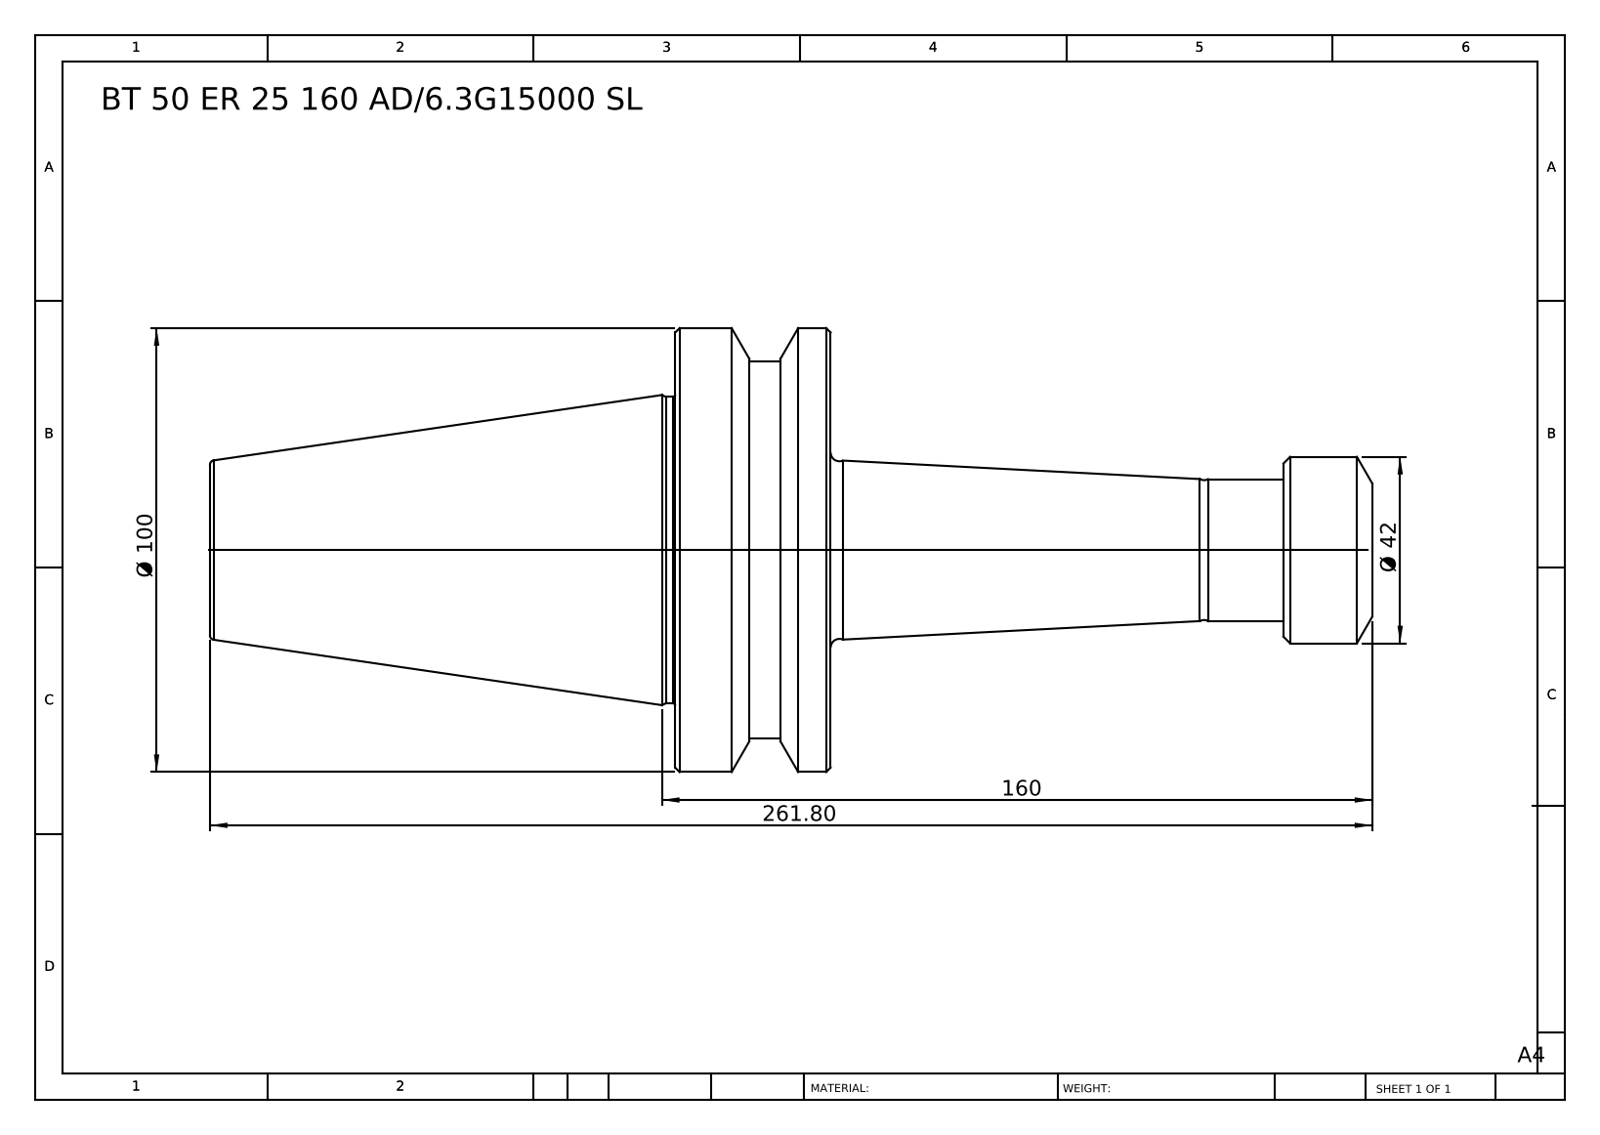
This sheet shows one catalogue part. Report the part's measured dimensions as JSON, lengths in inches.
{"part_name": "BT 50 ER 25 160 AD-6.3G15000 SL", "step_written_by": "SolidWorks 2014 (CONFIG_CONTROL_DESIGN)", "units": "inches", "bodies": {"solids": 1, "faces": 51, "planar": 7, "cylindrical": 12, "other": 32}, "overall_size": [10.307, 3.937, 3.937], "volume_in3": 38.93, "surface_area_in2": 90.72, "round_bosses_or_shafts": [[3.937, 1], [3.346, 1], [2.717, 1], [1.654, 1], [1.256, 1]], "face_to_face_distances": [1.378, 5.504, 4.126, 4.803, 6.181, 10.307, 0.787, 4.016, 5.394, 9.52]}
